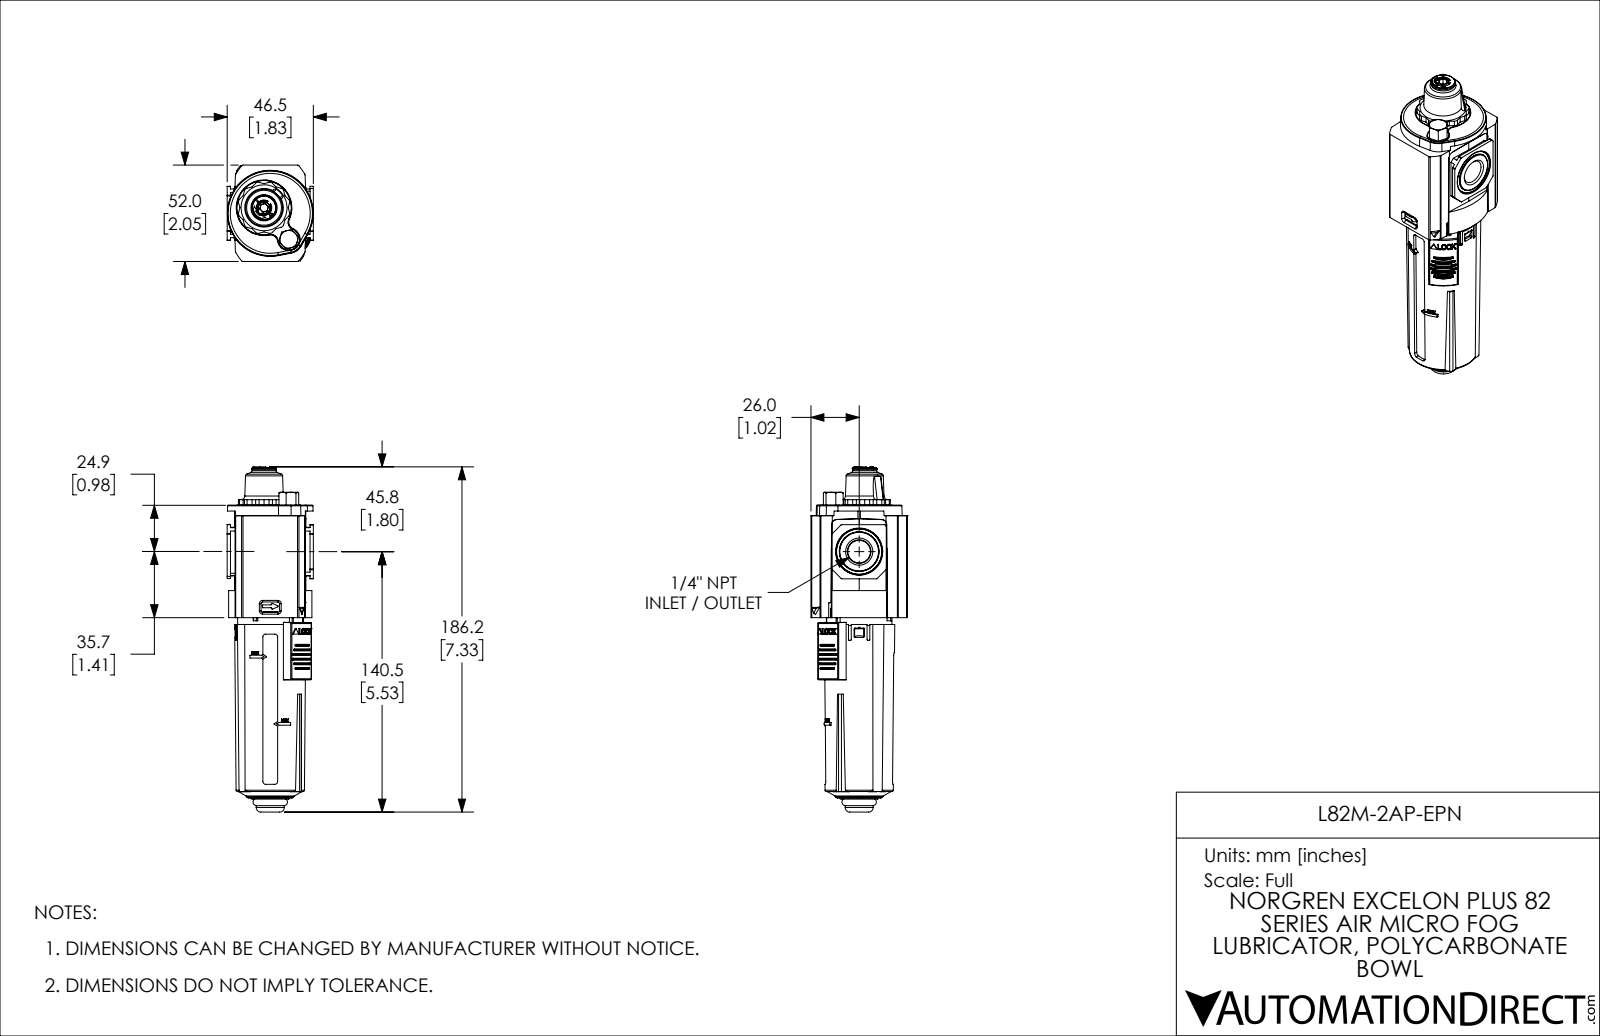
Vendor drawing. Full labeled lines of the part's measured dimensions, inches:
Part name (STEP PRODUCT): L82M-2AP-EPN
STEP written by: SolidWorks 2021 (CONFIG_CONTROL_DESIGN)
Units: inches
Bodies: 7 solids, 1298 faces (592 planar, 456 cylindrical, 250 other)
Overall size (bounding box): 7.331 × 2.047 × 1.831
Volume: 13.15 in³ · Surface area: 94.76 in²
Round holes (diameter × count): ⌀0.271 ×1, ⌀0.312 ×1, ⌀0.312 ×1, ⌀0.354 ×1, ⌀0.63 ×1, ⌀0.943 ×1, ⌀1.181 ×1
Round bosses / shafts (diameter × count): ⌀0.24 ×2, ⌀1.388 ×1, ⌀1.356 ×1, ⌀1.291 ×1, ⌀1.257 ×1, ⌀1.161 ×1, ⌀0.906 ×1, ⌀0.626 ×1
Partial cylindrical surfaces — rounded edges, fillets, slot ends (radius × count): R0.02 ×58, R0.039 ×30, R0.008 ×22, R0.01 ×12, R0.075 ×12, R0.012 ×11, R0.059 ×10, R0.118 ×9
Main face-to-face distances: 0.059, 1.988, 2.047, 1.929, 0.236, 1.352, 0.182, 1.475, 1.417, 1.293
Hole centre spacings: 0.177, 0.677, 0.851
